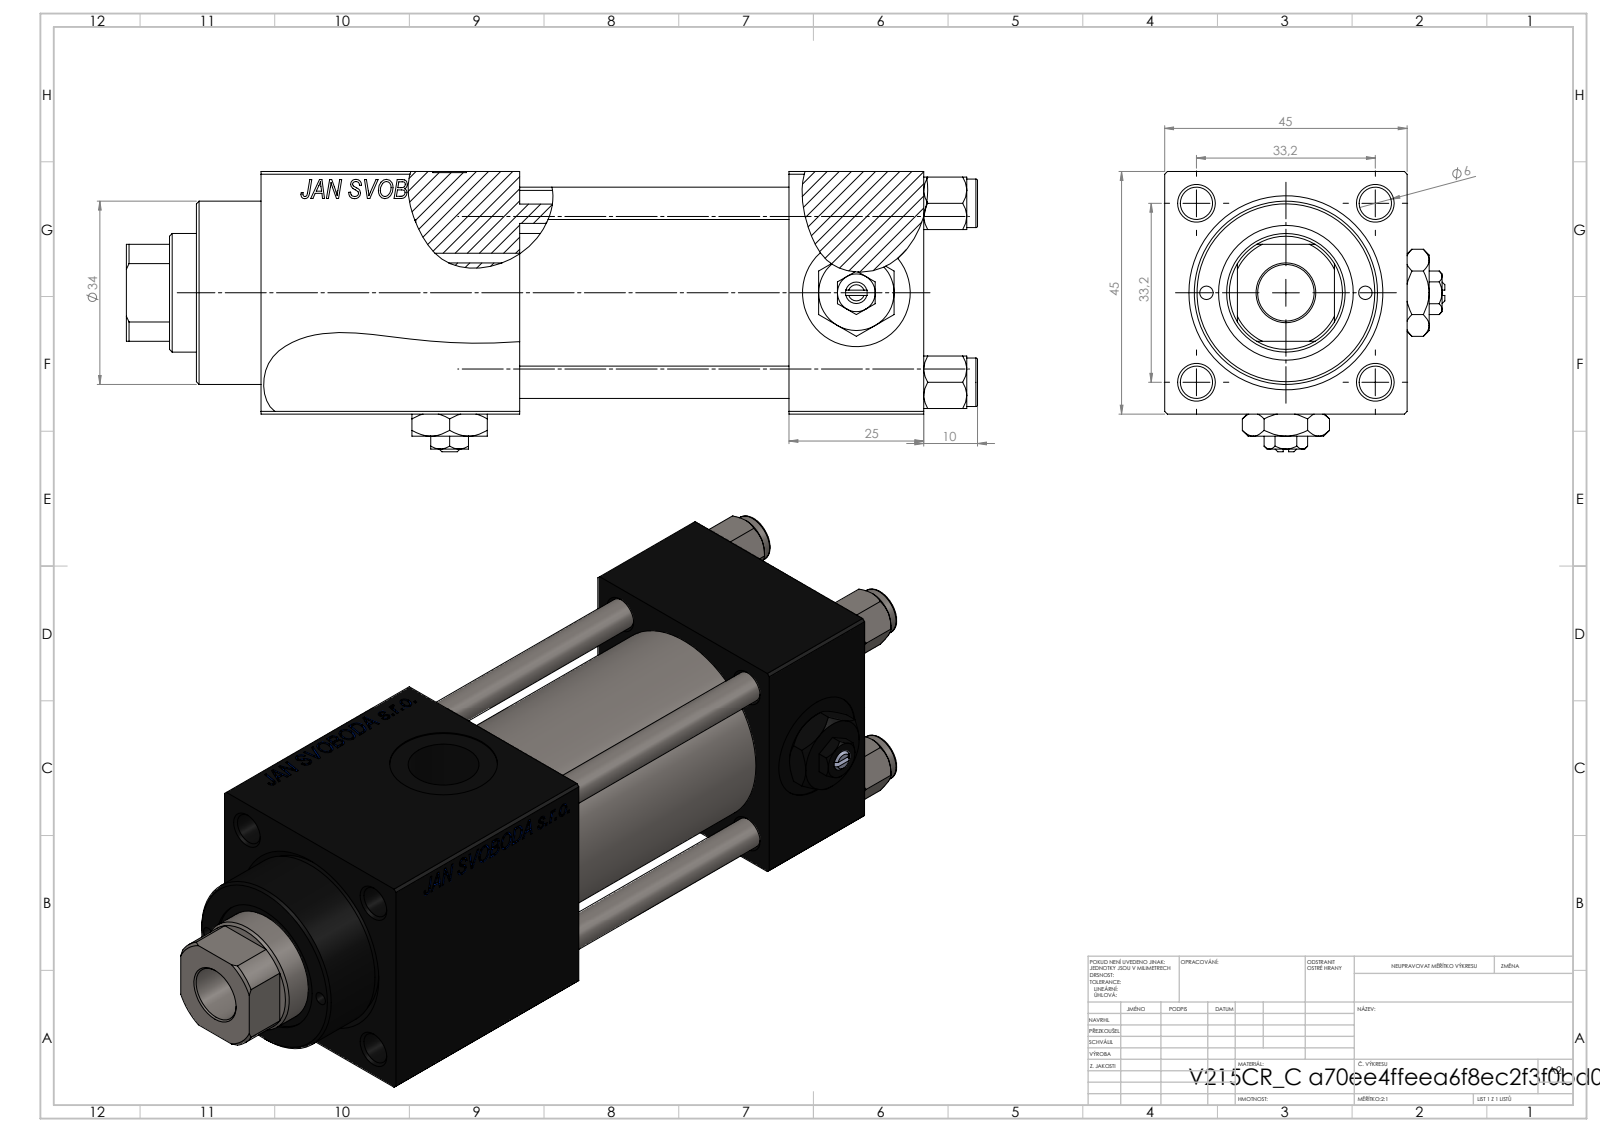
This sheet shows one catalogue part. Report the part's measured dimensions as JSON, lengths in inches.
{"part_name": "V215CR_VCP_C; V215CR_C_TYCINKA; NUT_M5_C; V215CR_C_Body (+2 more)", "step_written_by": "SolidWorks 2019 (CONFIG_CONTROL_DESIGN)", "units": "inches", "bodies": {"solids": 13, "faces": 1254, "planar": 574, "cylindrical": 102, "other": 578}, "overall_size": [6.22, 2.047, 2.047], "volume_in3": 12.7, "surface_area_in2": 113.8, "round_holes": [[0.236, 4], [0.098, 2], [0.276, 2], [0.518, 2], [0.787, 2], [0.413, 1], [0.866, 1], [0.945, 1], [0.984, 1], [1.26, 1], [1.299, 1]], "round_bosses_or_shafts": [[0.354, 4], [1.496, 1], [1.339, 1]], "partial_cylinders_radius": [[0.413, 1]], "face_to_face_distances": [1.772, 0.984, 1.969, 4.843, 2.953, 3.858, 1.764, 1.89, 3.713, 2.728], "hole_center_spacings": [0.657, 0.924, 1.307, 1.396, 0.581, 1.848, 1.161]}
